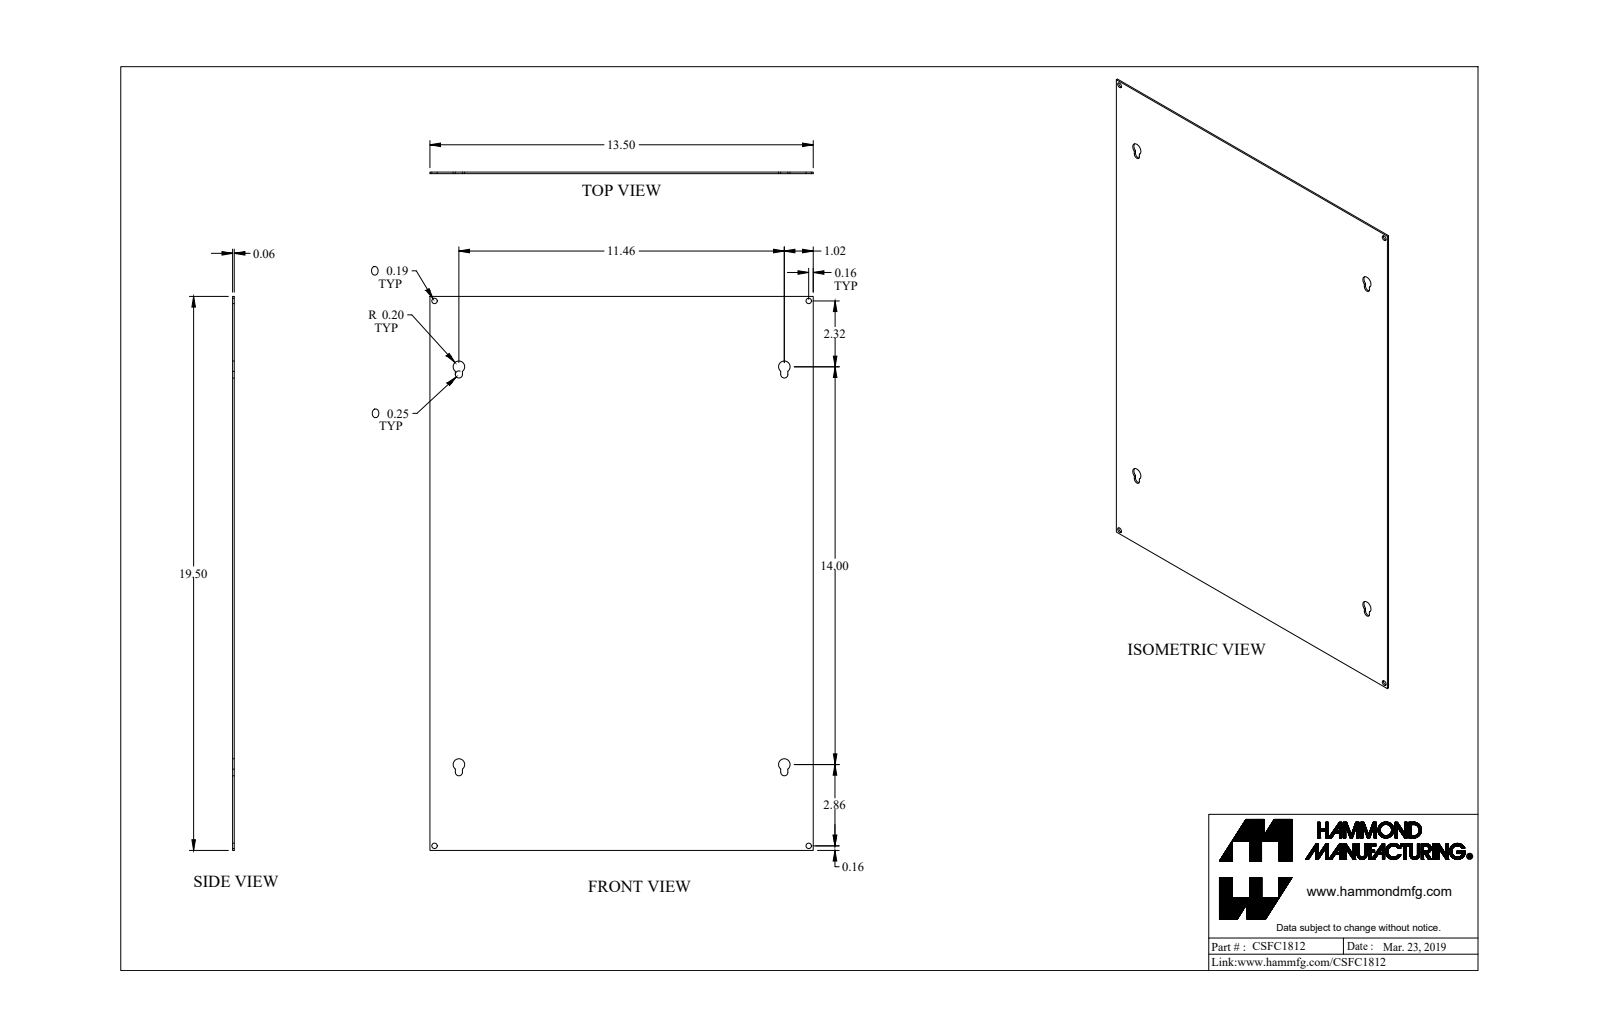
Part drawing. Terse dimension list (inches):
name: CSFC1812_Default
written by: SolidWorks 2019 (CONFIG_CONTROL_DESIGN)
unit: in
bodies: 1 solid, 38 faces (14 planar, 24 cylindrical, 0 other)
size: 19.5 × 13.5 × 0.057
volume: 14.96 in³; area: 529.1 in²
holes: 4× ⌀0.188
rounds: 4× R0.125, 4× R0.203
face distances: 0.057, 13.5, 19.5, 1.145, 12.355, 0.895, 12.605, 11.46, 0.25, 11.71
hole spacings: 13.18, 19.18, 23.272
